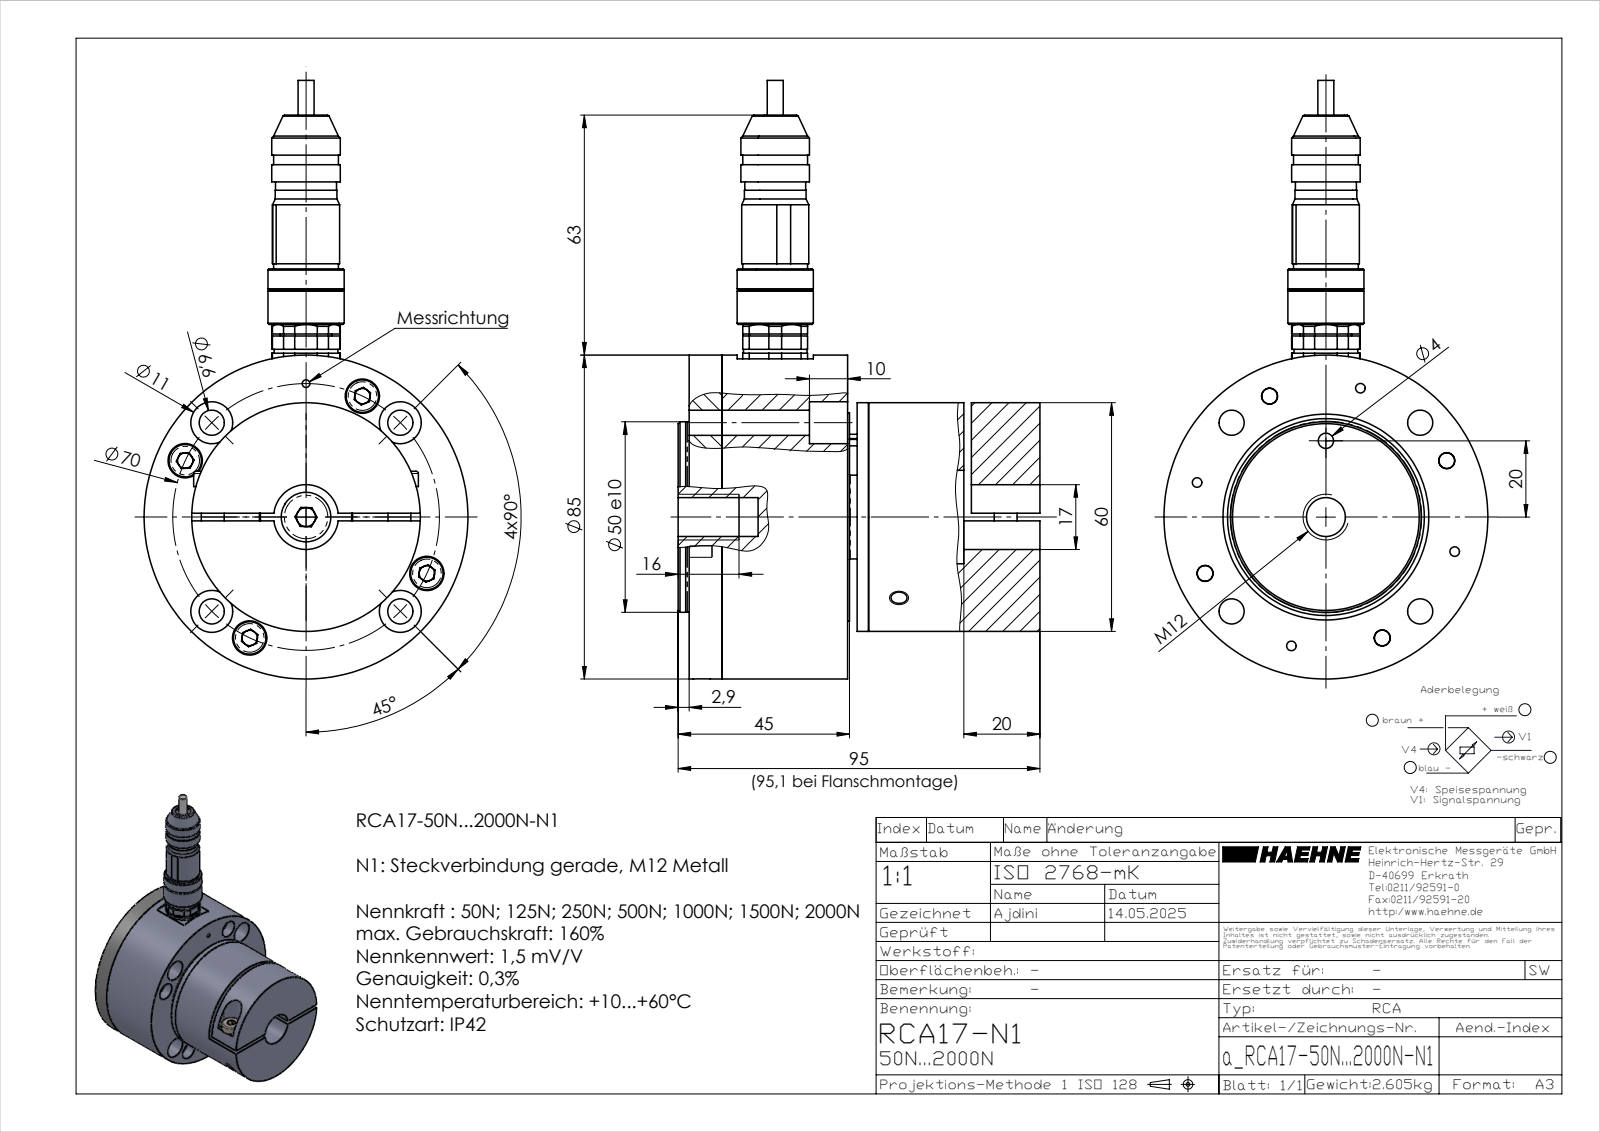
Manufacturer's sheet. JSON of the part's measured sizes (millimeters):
{"part_name": "inafag_1203-tvh_7zkvytp7yxkimpdvw8sj0b5w4_15; inafag_1203-tvh_7zkvytp7yxkimpdvw8sj0b5w4_09; inafag_1203-tvh_7zkvytp7yxkimpdvw8sj0b5w4_25; a_RCA17-50N...2000N-N1_Flansch (+8 more)", "step_written_by": "SolidWorks 2023 (AUTOMOTIVE_DESIGN)", "units": "millimeters", "bodies": {"solids": 54, "faces": 744, "planar": 378, "cylindrical": 203, "other": 163}, "overall_size": [157.06, 95.1, 85], "volume_mm3": 378214, "surface_area_mm2": 114438, "round_holes": [[3.4, 9], [2.5, 8], [6.6, 6], [1, 5], [4.2, 5], [4, 4], [5.3, 4], [9, 4], [11, 4], [4.5, 2], [5, 2], [2, 1]], "round_bosses_or_shafts": [[3, 9], [5.7, 8], [8.5, 4], [5, 4], [1.5, 4], [1, 4], [10, 2], [8, 2]], "partial_cylinders_radius": [[0.3, 6], [1, 4], [5.5, 2], [0.57, 1], [0.6, 1], [0.77, 1], [3.5, 1]], "face_to_face_distances": [3, 2, 8.6, 47.1, 45, 11.6, 30, 50, 35.5, 38.5], "hole_center_spacings": [35, 49.5, 24.78, 25.2, 32.8, 51.14, 56.46, 2.5]}
